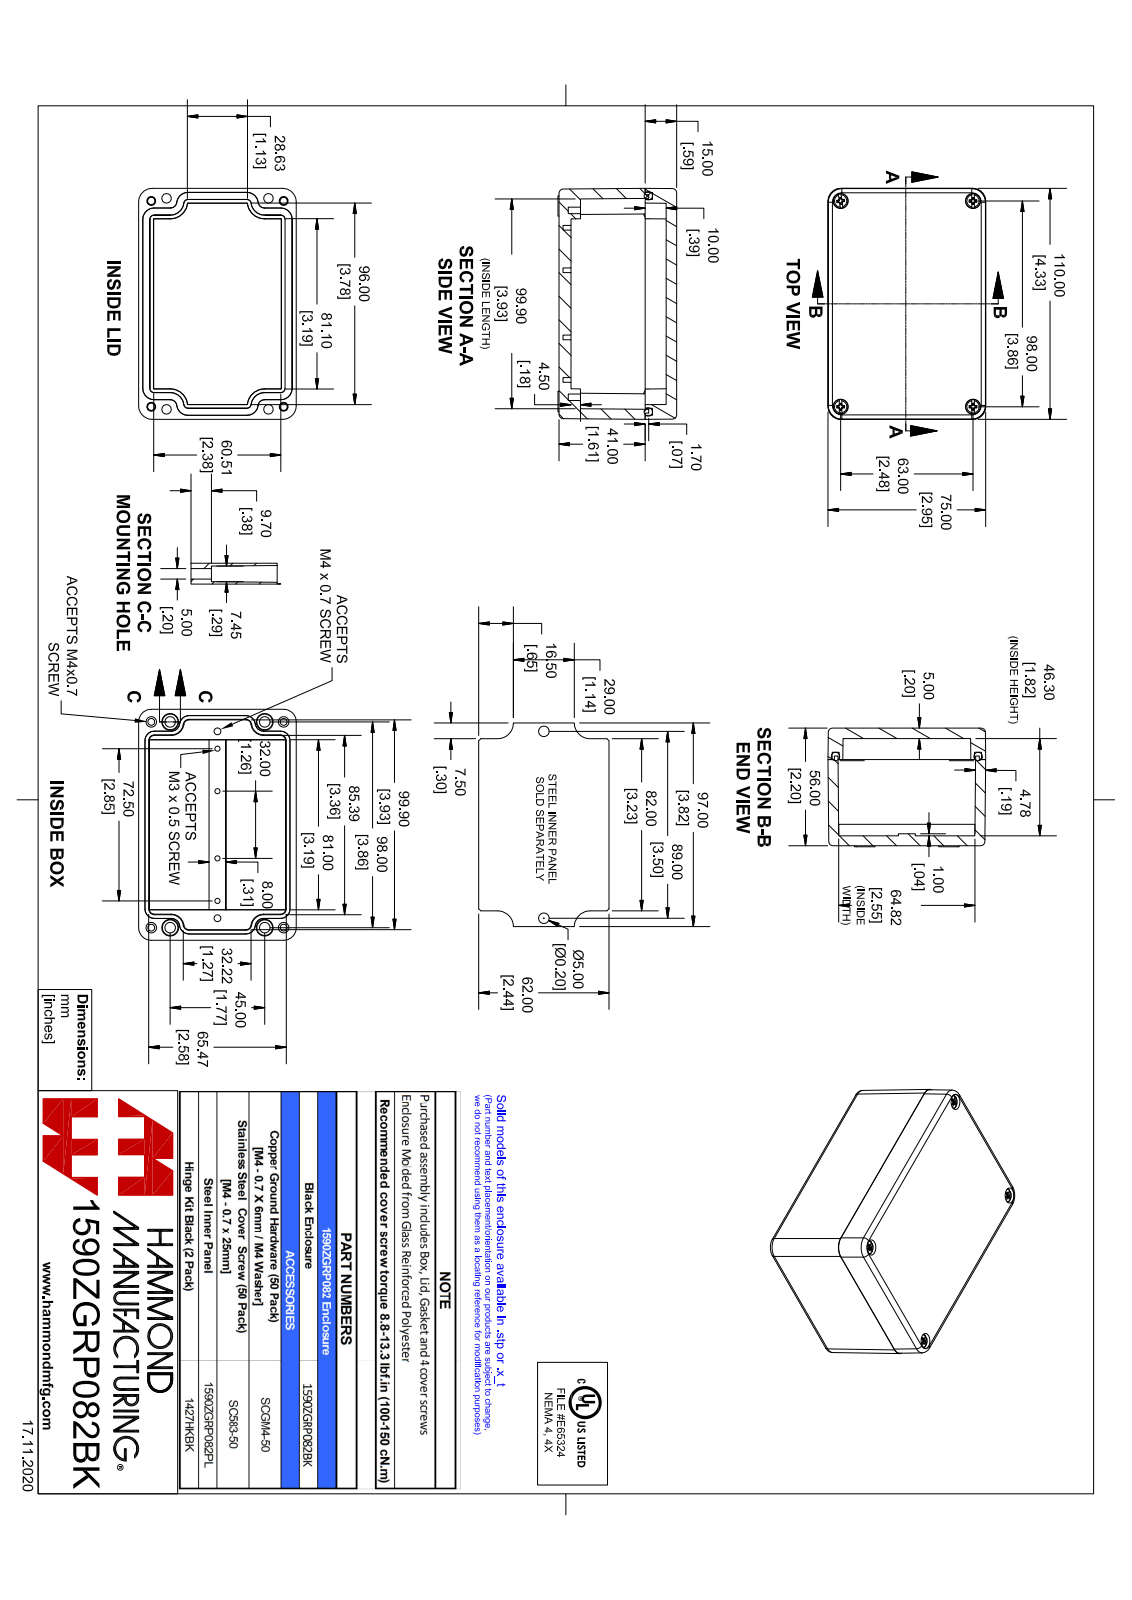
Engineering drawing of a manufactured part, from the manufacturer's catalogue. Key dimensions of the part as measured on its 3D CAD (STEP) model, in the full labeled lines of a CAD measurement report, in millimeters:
Part name (STEP PRODUCT): 1590ZGRP082BK
STEP written by: SolidWorks 2021 (AUTOMOTIVE_DESIGN)
Units: millimetres
Bodies: 7 solids, 449 faces (247 planar, 82 cylindrical, 120 other)
Overall size (bounding box): 110 × 75 × 56.5
Volume: 176 800 mm³ · Surface area: 81 550 mm²
Round holes (diameter × count): ⌀5 ×8, ⌀3.3 ×6, ⌀3.5 ×4, ⌀4.5 ×4, ⌀7.2 ×4, ⌀2.5 ×3, ⌀2.5 ×1
Round bosses / shafts (diameter × count): ⌀4 ×6, ⌀6.9 ×4, ⌀3.9 ×4, ⌀3.5 ×4
Partial cylindrical surfaces — rounded edges, fillets, slot ends (radius × count): R1 ×16, R2 ×8, R6 ×4, R6.5 ×4
Main face-to-face distances: 4.8, 56, 5, 51, 4, 47, 52, 15, 41, 37.1
Hole centre spacings: 2.2, 7.4, 9, 23, 24.9, 25.9, 28, 31.8
